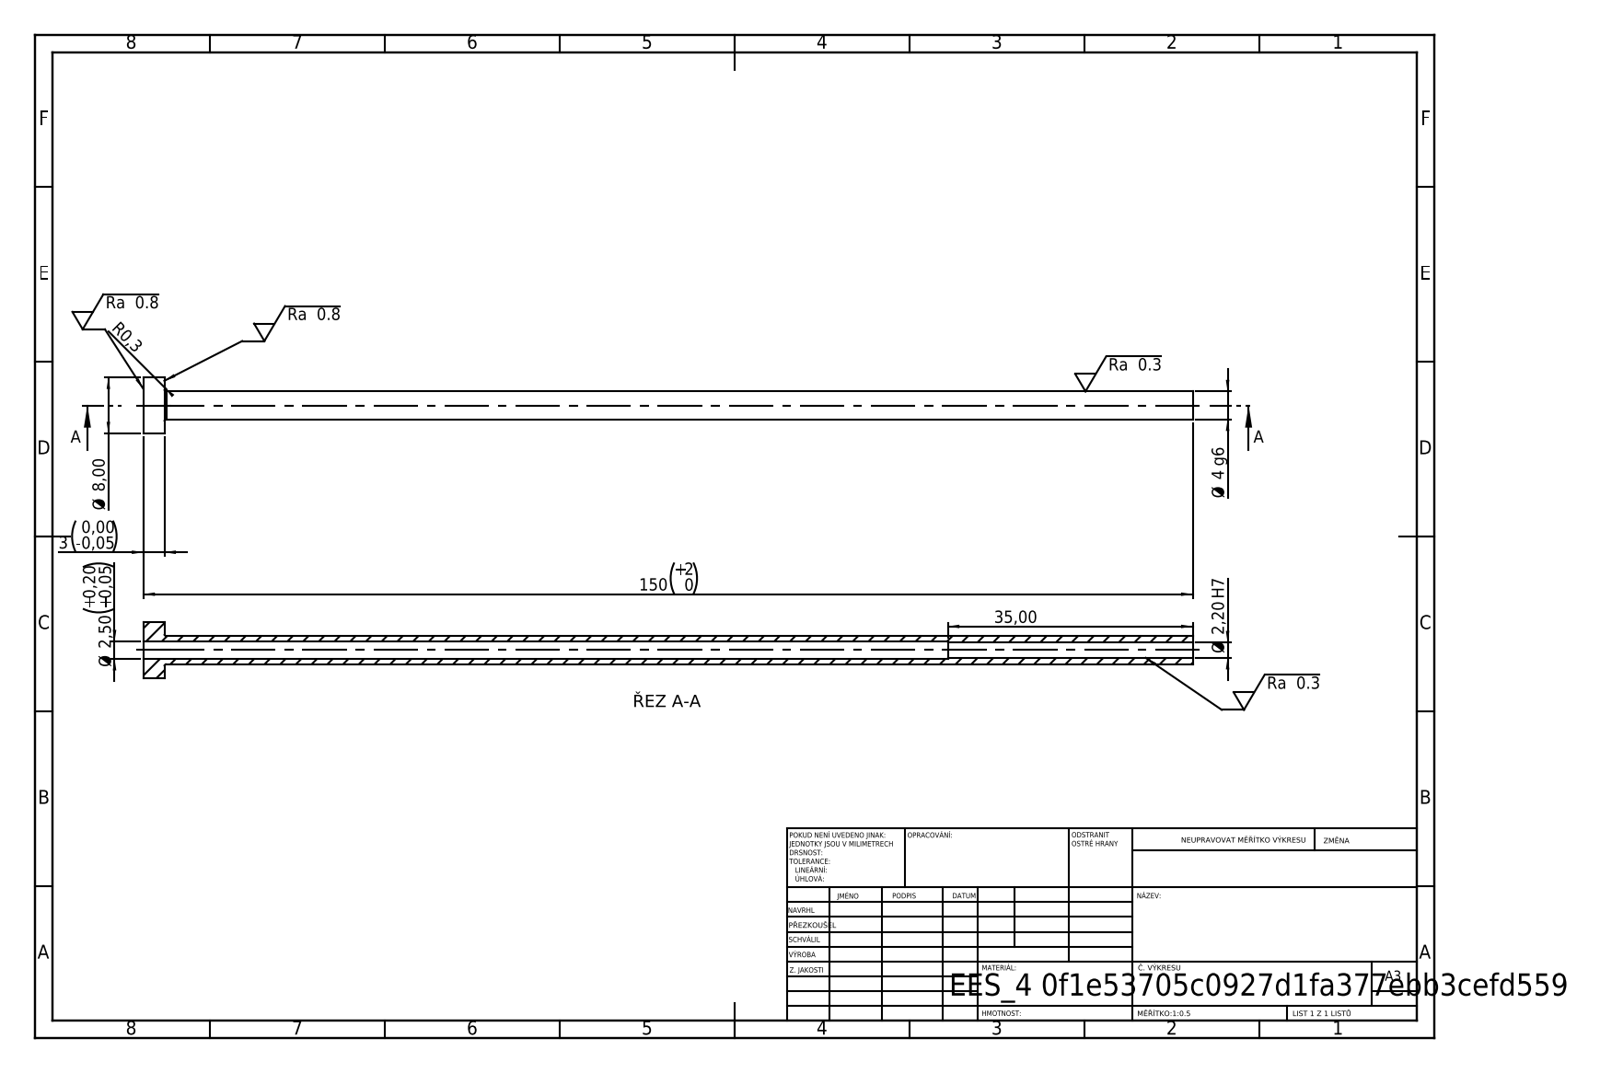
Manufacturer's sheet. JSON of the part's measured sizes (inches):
{"step_written_by": "SolidWorks 2019 (CONFIG_CONTROL_DESIGN)", "units": "inches", "bodies": {"solids": 1, "faces": 14, "planar": 4, "cylindrical": 8, "other": 2}, "overall_size": [5.906, 0.315, 0.315], "volume_in3": 0.079, "surface_area_in2": 4.896, "round_holes": [[0.087, 1], [0.098, 1]], "round_bosses_or_shafts": [[0.315, 1], [0.157, 1]], "face_to_face_distances": [0.118, 5.906, 5.787, 4.528, 4.409, 1.378]}
